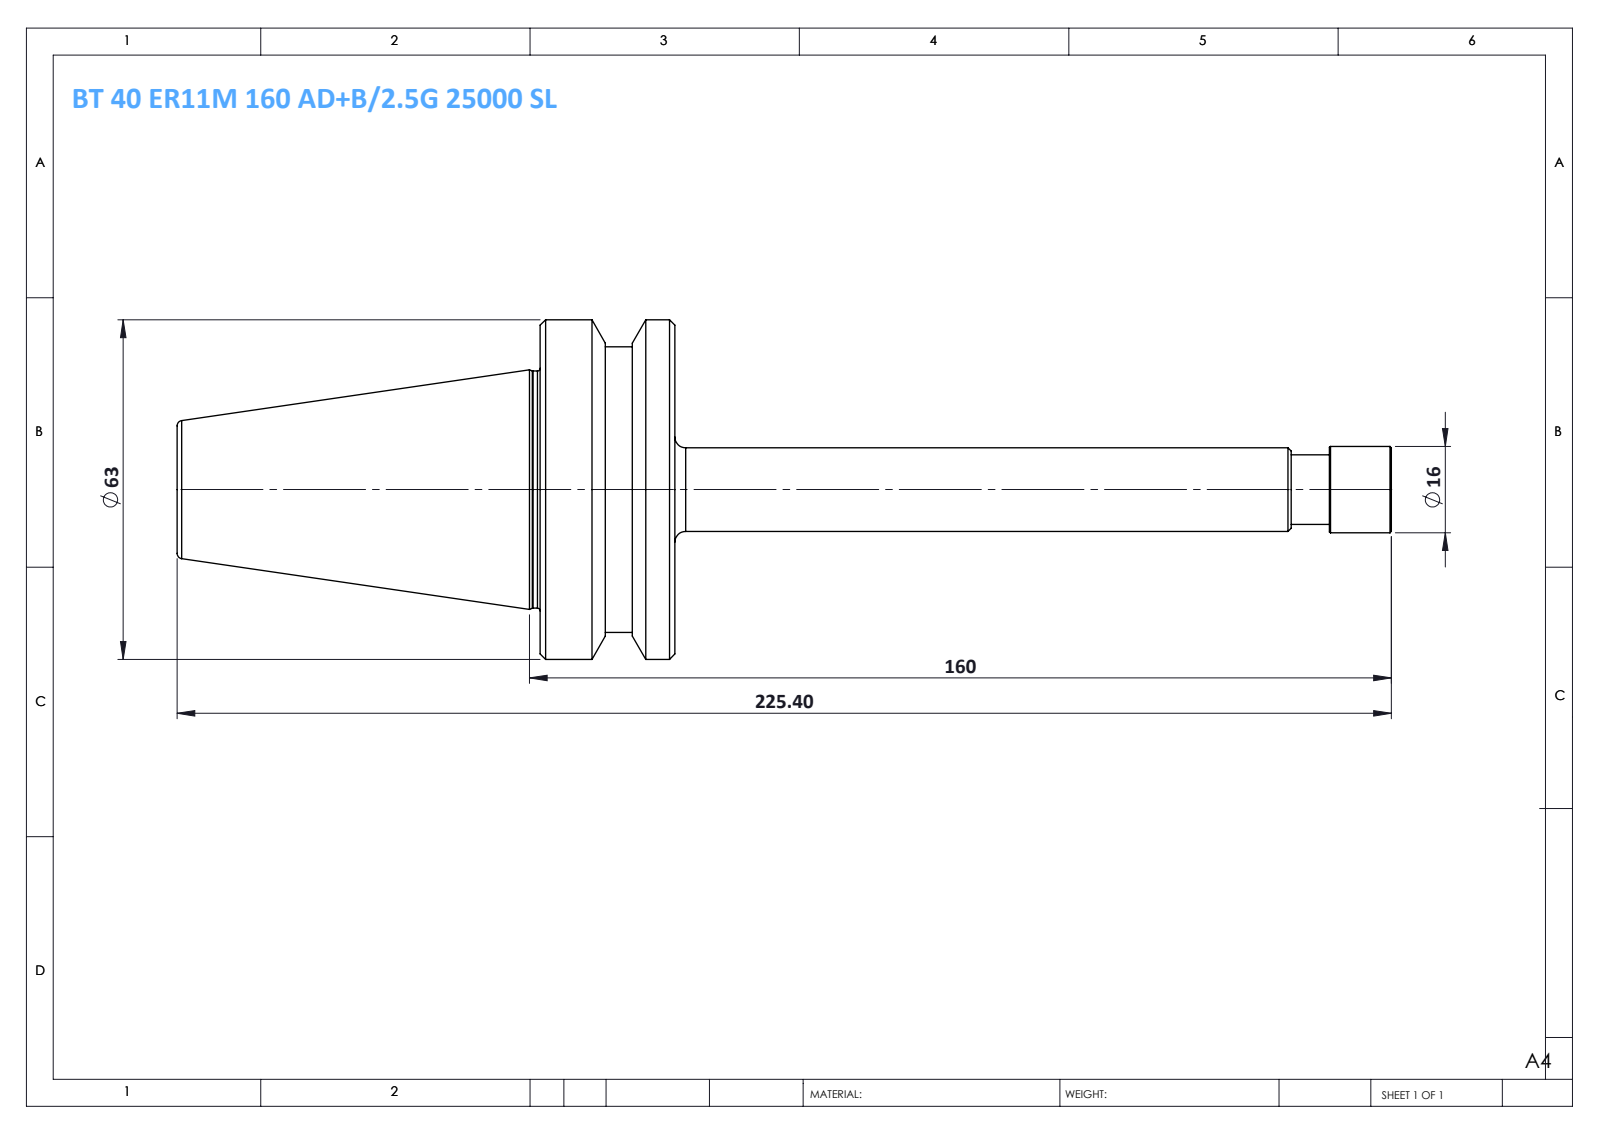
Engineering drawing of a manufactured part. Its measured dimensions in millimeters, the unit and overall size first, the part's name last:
Units: millimetres
Overall size (bounding box): 225.4 × 63 × 63
Round bosses / shafts (diameter × count): ⌀63 ×1, ⌀53 ×1, ⌀44 ×1, ⌀16 ×1, ⌀15.5 ×1, ⌀12.9 ×1
Main face-to-face distances: 25, 92.4, 67.4, 133, 158, 225.4, 140.9, 145.9, 7.9, 12.9
Volume: 163 207 mm³ · Surface area: 24 840 mm²
Bodies: 1 solid, 48 faces (8 planar, 14 cylindrical, 26 other)
Part name (STEP PRODUCT): BT 40 ER11M 160 AD+B-2.5G 25000 SL
STEP written by: SolidWorks 2014 (CONFIG_CONTROL_DESIGN)
